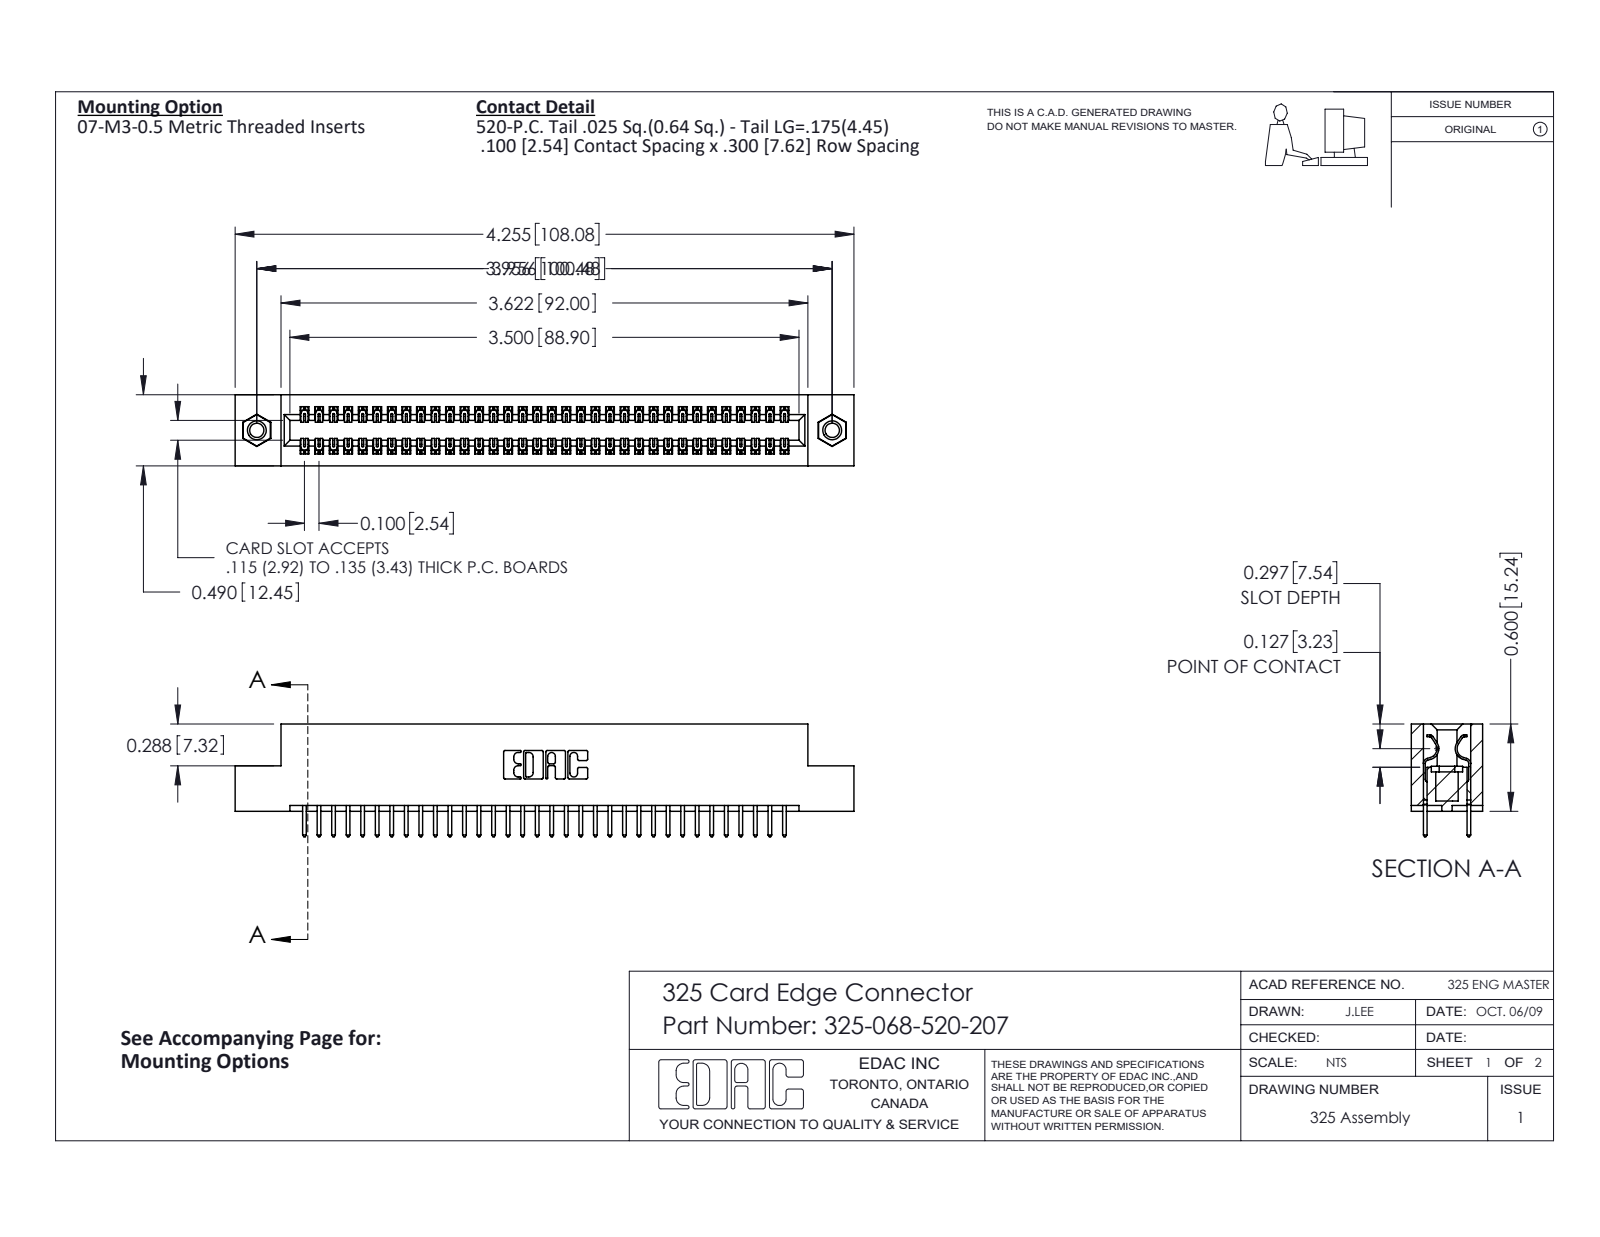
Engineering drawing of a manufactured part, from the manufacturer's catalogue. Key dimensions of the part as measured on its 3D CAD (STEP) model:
Part name (STEP PRODUCT): 345-250-001_345-250-005-103; 325-292-001_325-293-120; 325-068-520-207; 325 Part_TI
STEP written by: SolidWorks 2016 (CONFIG_CONTROL_DESIGN)
Units: inches
Bodies: 71 solids, 3710 faces (2550 planar, 1144 cylindrical, 16 other)
Overall size (bounding box): 4.255 × 0.775 × 0.49
Volume: 0.846 in³ · Surface area: 25.53 in²
Round holes (diameter × count): ⌀0.098 ×2, ⌀0.125 ×2, ⌀0.16 ×2
Round bosses / shafts (diameter × count): ⌀0.155 ×2
Partial cylindrical surfaces — rounded edges, fillets, slot ends (radius × count): R0.006 ×102, R0.01 ×68, R0.01 ×22, R0.007 ×6, R0.031 ×6, R0.026 ×3, R0.014 ×2, R0.022 ×2
Main face-to-face distances: 0.083, 0.407, 0.3, 0.49, 0.107, 0.383, 0.025, 0.325, 0.04, 0.275
Hole centre spacings: 3.956
